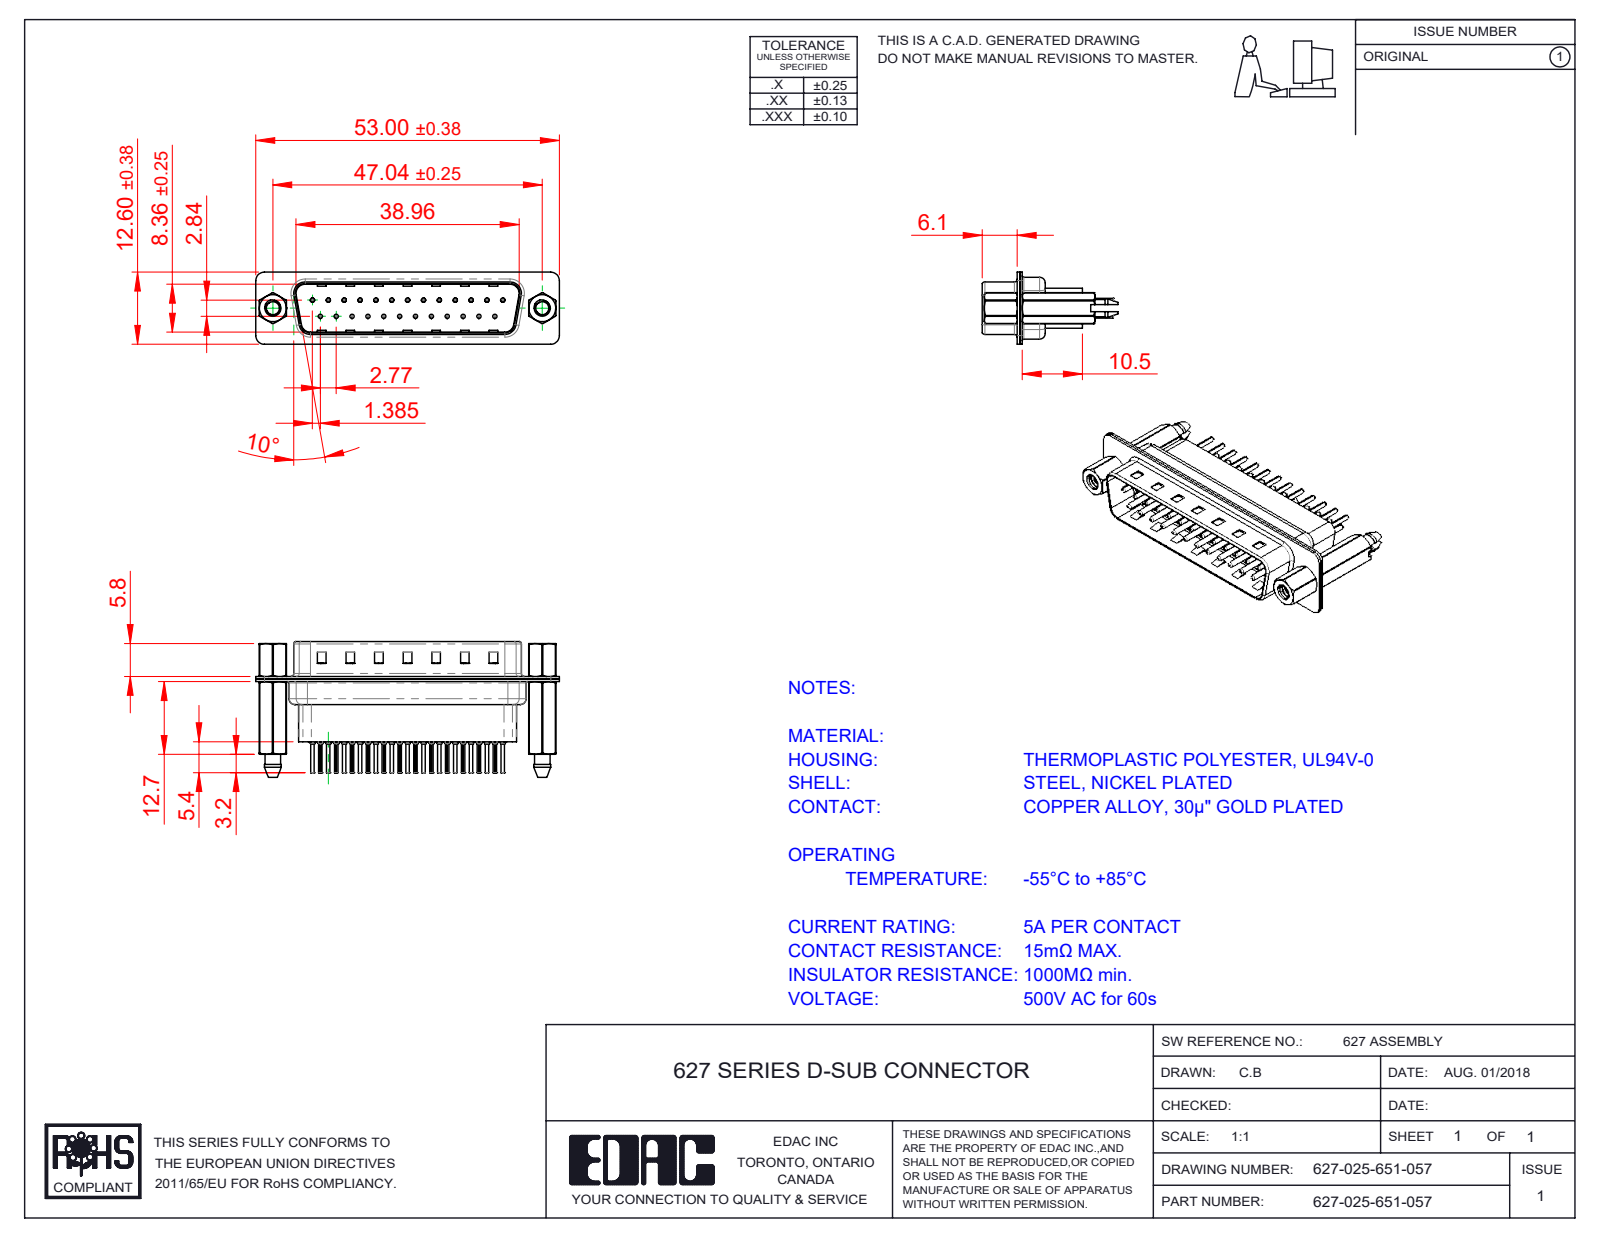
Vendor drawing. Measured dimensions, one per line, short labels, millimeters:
name: 627 4-40 Hex Standoff; 627 Shell Front_25 Contacts; 627 Shell Rear_25 Contacts; 627 4-40 Threaded Boardlock_HP51 (+4 more)
written by: SolidWorks 2020 (CONFIG_CONTROL_DESIGN)
unit: mm
bodies: 32 solids, 3060 faces (825 planar, 1200 cylindrical, 1035 other)
size: 53 × 23.6 × 12.6
volume: 4 334 mm³; area: 11 076 mm²
holes: 25× ⌀0.2, 25× ⌀0.35, 25× ⌀1.1, 25× ⌀1.6, 2× ⌀2.26, 2× ⌀2.29, 2× ⌀4, 2× ⌀4.8
bosses: 25× ⌀2, 25× ⌀1.5, 25× ⌀0.75, 25× ⌀0.6, 2× ⌀4.9, 2× ⌀2.79
rounds: 50× R0.1, 18× R1.5, 12× R2, 10× R1.6, 8× R0.5, 4× R0.25, 4× R0.6, 4× R0.65
face distances: 0.4, 0.45, 0.82, 9.58, 0.68, 7.68, 1.5, 0.9, 1.08, 8.08
hole spacings: 3.16, 8.31, 2.77, 5.54, 11.08, 16.62, 5.03, 5.04
